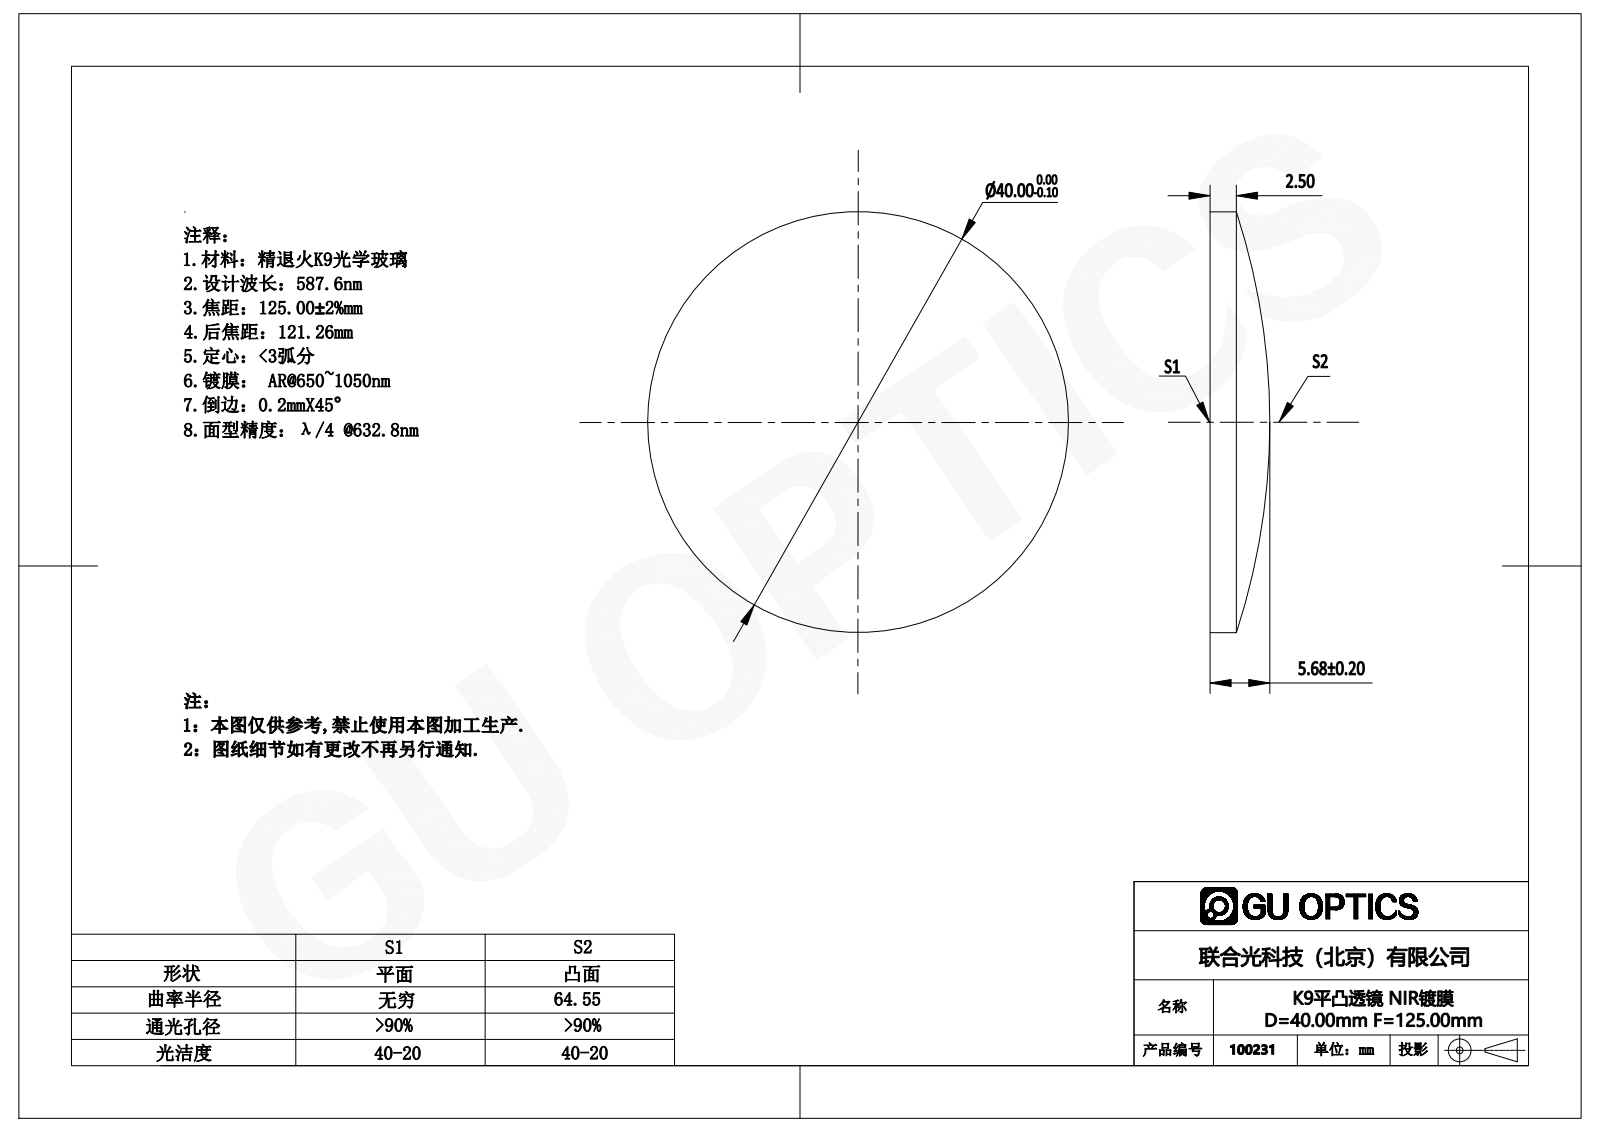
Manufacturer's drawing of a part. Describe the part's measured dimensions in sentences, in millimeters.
The part is named "100231". Its 3-D file was written by "SolidWorks 2016 (AUTOMOTIVE_DESIGN)". It is 1 solid with 5 faces: 1 planar, 2 cylindrical and 2 other. Overall it measures 40 by 40 by 5.68 millimeters. Its volume is 5 156 cubic millimeters and its surface area 2 859 square millimeters. Round bosses or shafts: 1 of diameter 40.
